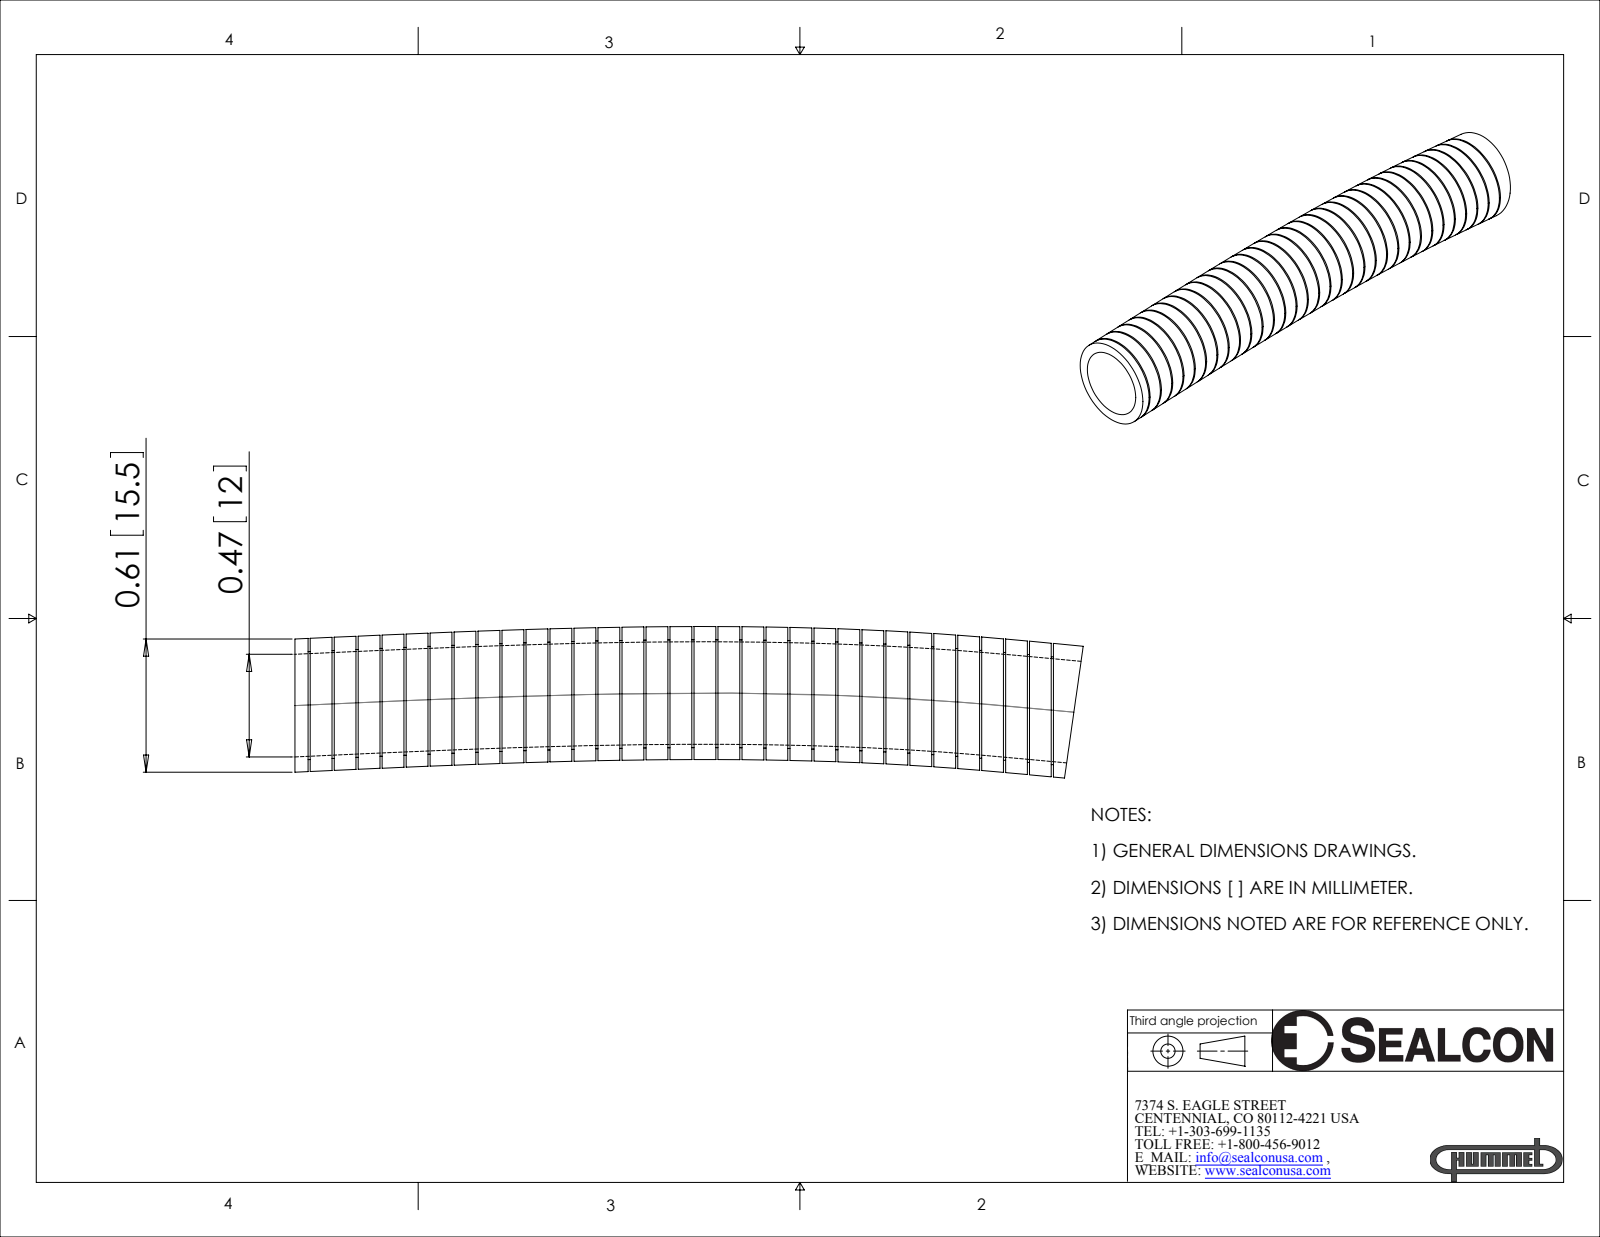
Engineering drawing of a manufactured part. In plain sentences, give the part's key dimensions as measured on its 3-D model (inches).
The part is named "SM-1013-HY". Its 3-D file was written by "SolidWorks 2007 (AUTOMOTIVE_DESIGN)". It is 1 solid with 198 faces: 66 planar, 64 cylindrical and 68 other. Overall it measures 3.613 by 0.694 by 0.61 inches. Its volume is 0.392 cubic inches and its surface area 18.68 square inches. Round bosses or shafts: 29 of diameter 0.494. The main face-to-face distances are 0.11, 0.219, 0.109, 0.12, 0.329, 0.1, 0.209, 0.229, 0.439, 0.339.
